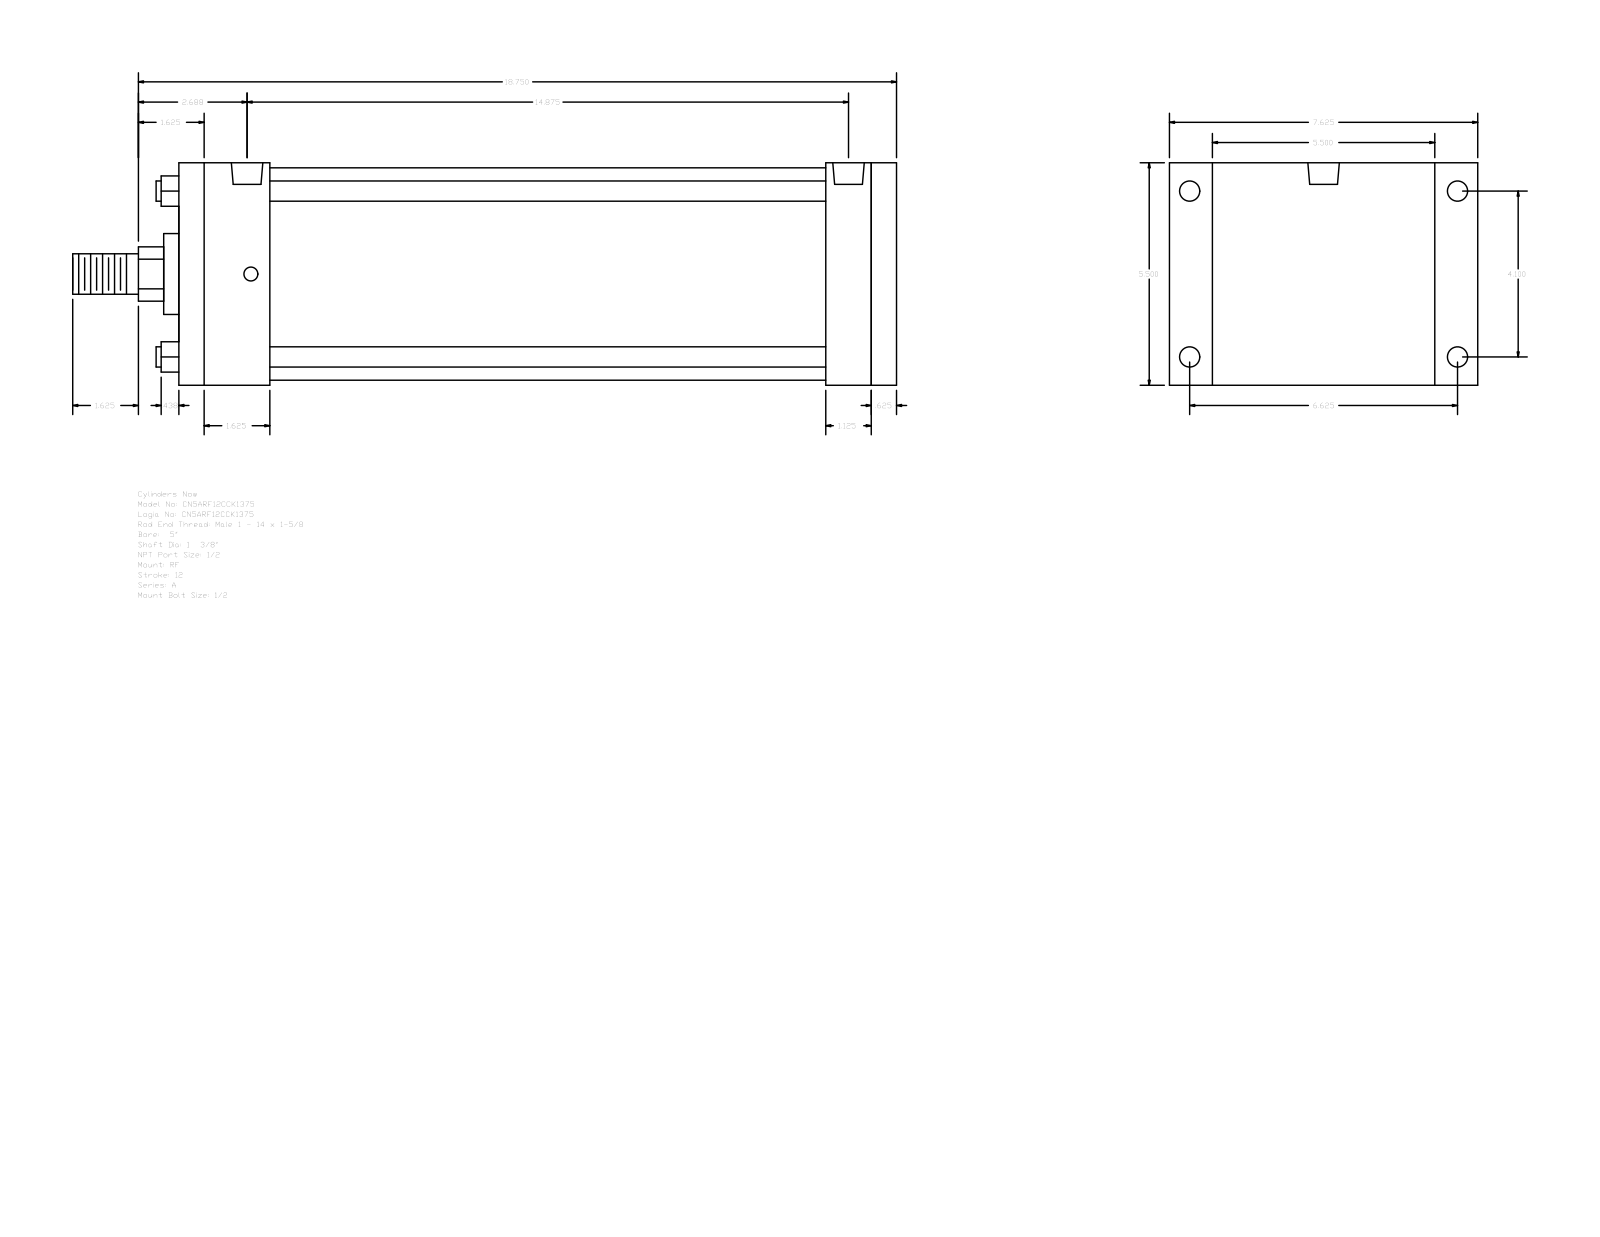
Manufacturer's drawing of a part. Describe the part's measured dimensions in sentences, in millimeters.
The part is named "A_RF__0500_1.375". Its 3-D file was written by "GSSL Pune (CONFIG_CONTROL_DESIGN)". It is 0 solids with 92 faces: 64 planar, 28 cylindrical and 0 other. Overall it measures 517.52 by 193.68 by 139.7 millimeters. Round holes: 4 of diameter 8.73, 4 of diameter 12.7, 2 of diameter 19.77. Round bosses or shafts: 4 of diameter 12.7, 1 of diameter 133.35, 1 of diameter 50.8, 1 of diameter 34.92, 1 of diameter 25.4. Partial cylindrical surfaces (rounded edges, fillets, slot ends): 1 of radius 17.06. The main face-to-face distances are 139.7, 450.85, 434.98, 15.87, 57.15, 28.58, 377.83, 393.7, 406.4, 349.25. The hole center spacings are 2.39, 104.14, 168.28, 197.9, 373.05, 375.44, 377.83.
